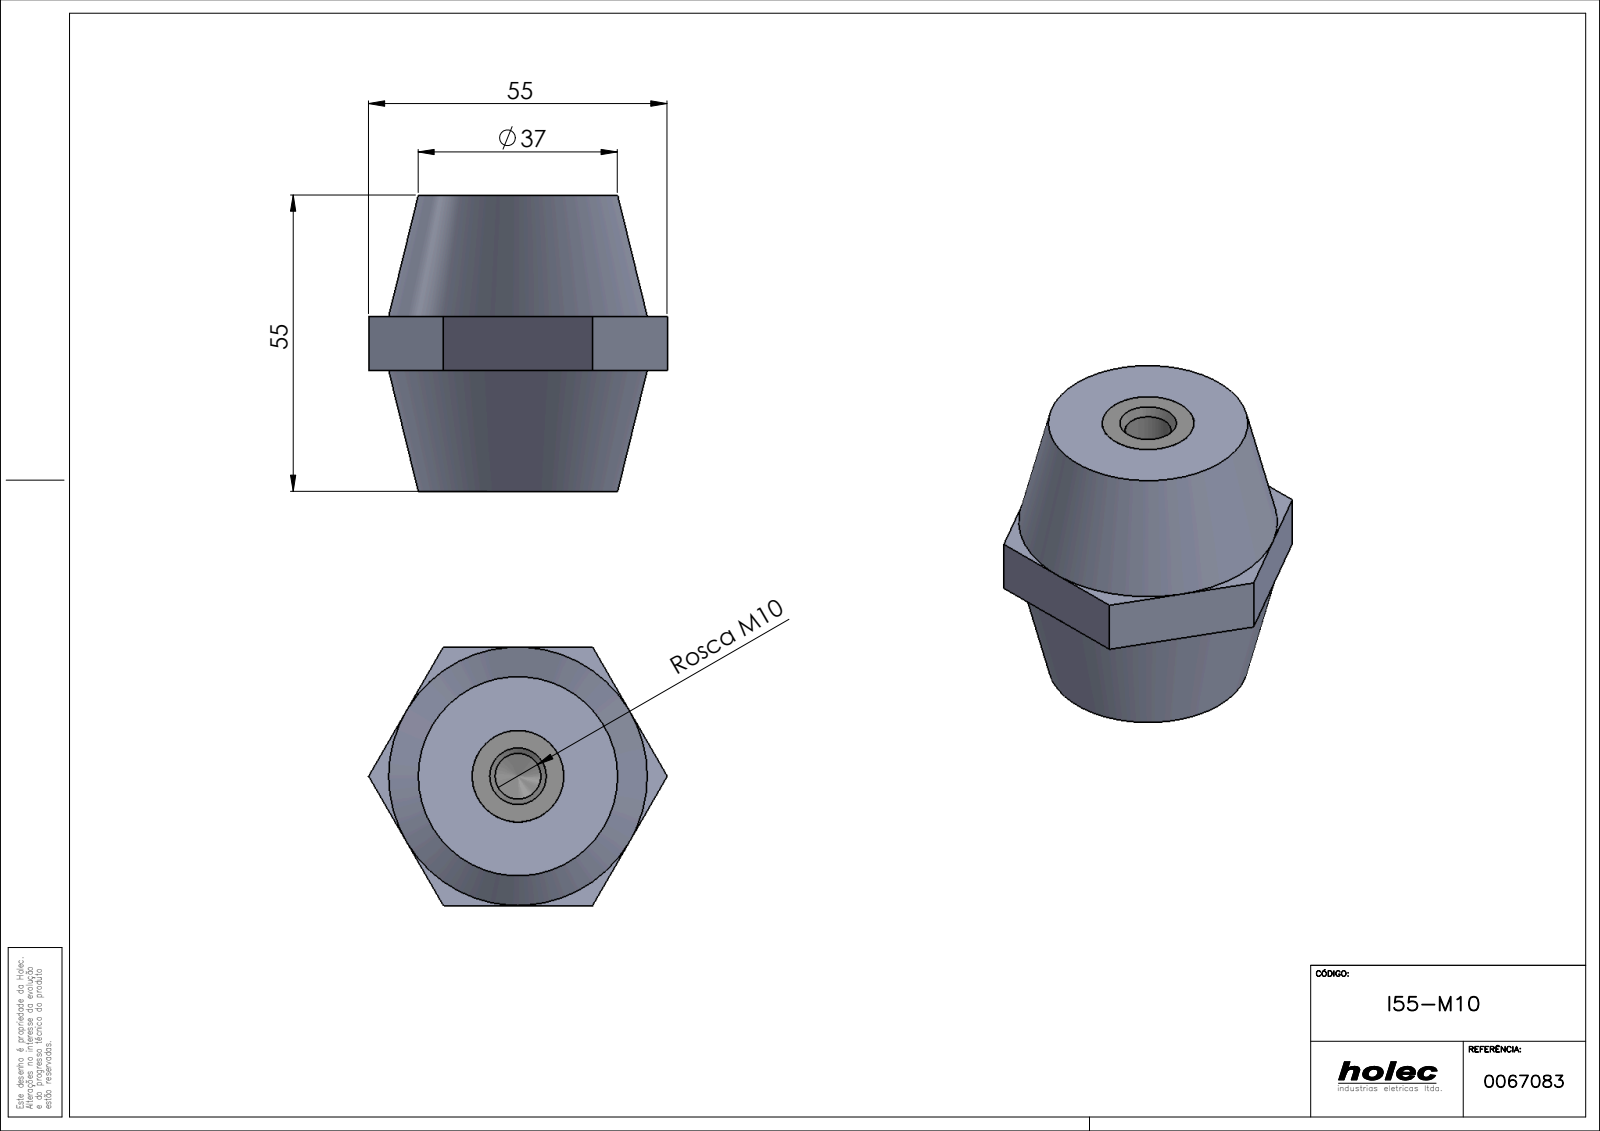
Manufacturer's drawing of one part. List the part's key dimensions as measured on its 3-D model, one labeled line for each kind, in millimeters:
Part name (STEP PRODUCT): PB1_0107(PB1_0106_10); I55-M10; PB1_0002
STEP written by: SolidWorks 2017 (AUTOMOTIVE_DESIGN)
Units: millimetres
Bodies: 3 solids, 162 faces (82 planar, 12 cylindrical, 68 other)
Overall size (bounding box): 55.43 × 55 × 48
Volume: 82 427 mm³ · Surface area: 16 416 mm²
Round holes (diameter × count): ⌀8.5 ×1, ⌀14 ×1
Main face-to-face distances: 17, 55, 38.01, 48, 38, 5, 12, 16.99, 21.01, 11.99
